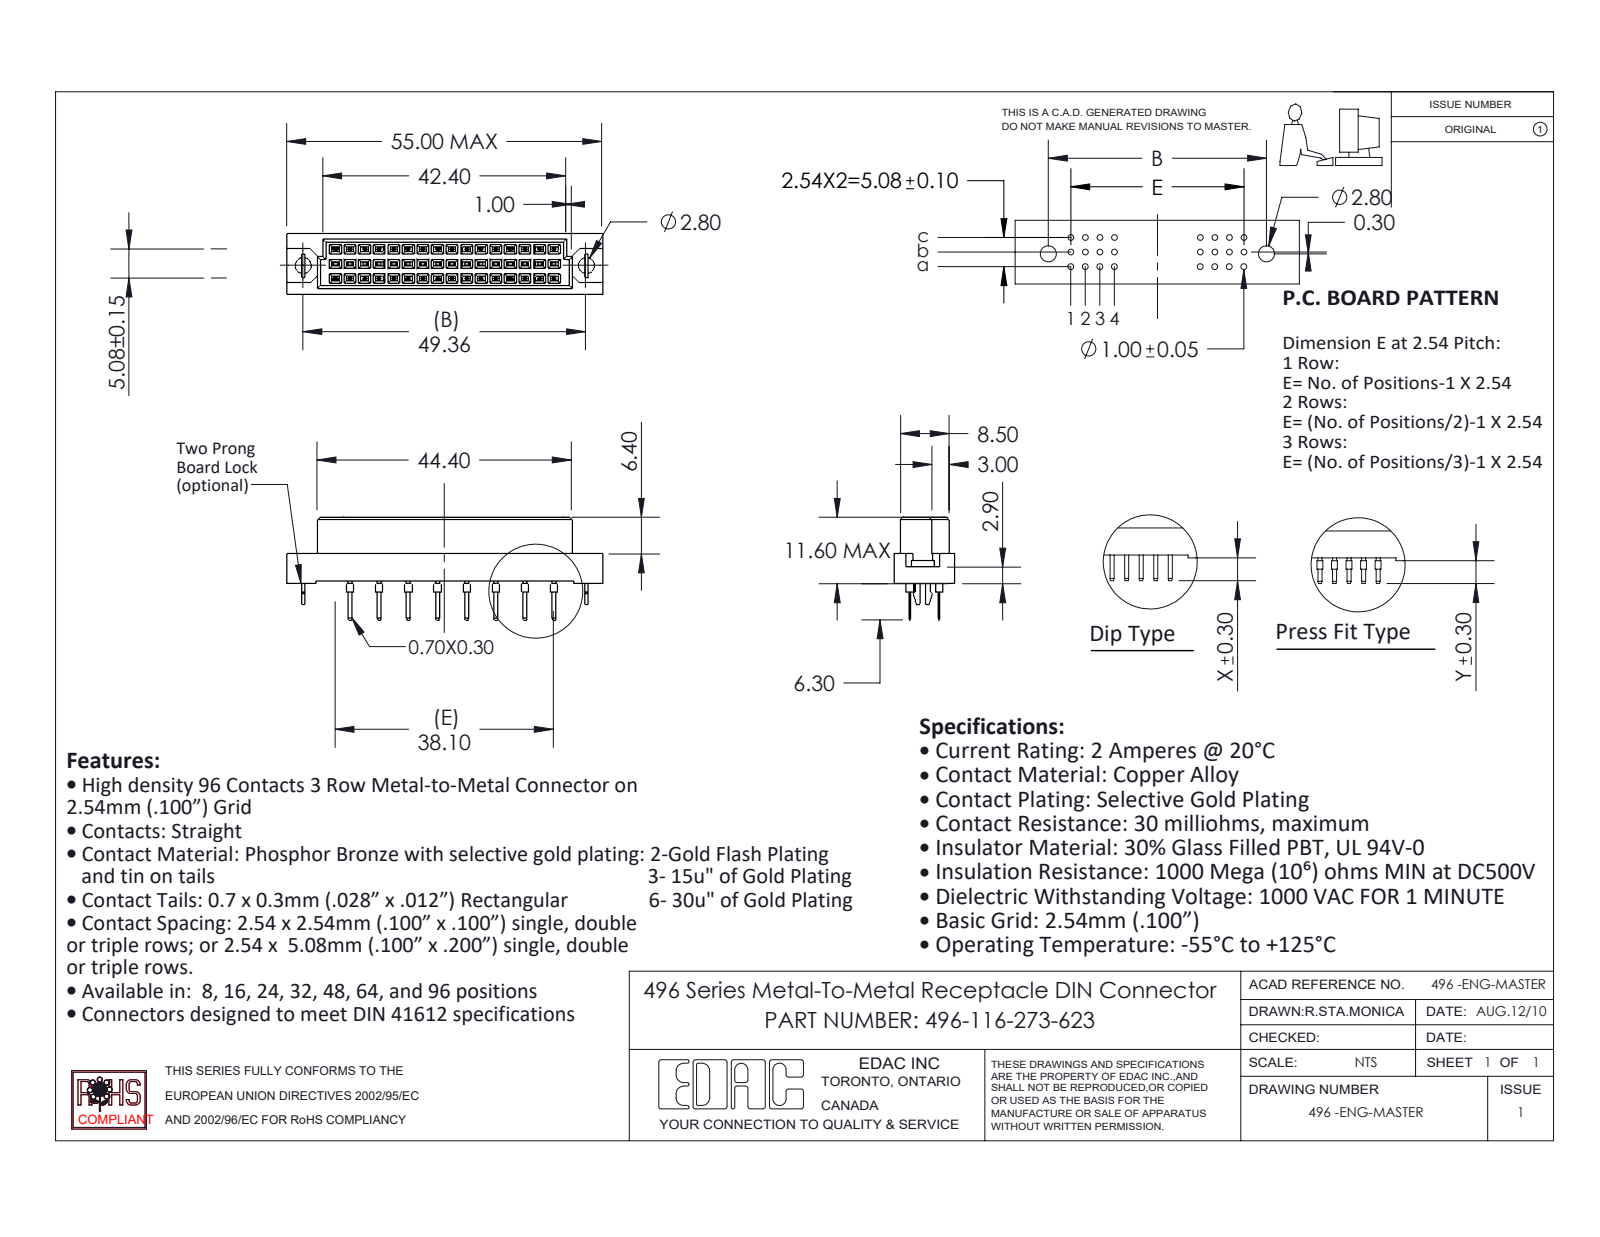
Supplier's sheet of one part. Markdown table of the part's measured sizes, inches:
| quantity | value |
| --- | --- |
| part name | 496 Part_48; 496-116-273-623; 496-290_73; 496 Bore-lock |
| STEP written by | SolidWorks 2020 (CONFIG_CONTROL_DESIGN) |
| units | inches |
| bodies | 19 solids, 990 faces (952 planar, 38 cylindrical, 0 other) |
| overall size | 2.165 × 0.705 × 0.417 |
| volume | 0.284 in³ |
| surface area | 7.318 in² |
| round holes (diameter × count) | 0.11 × 2 |
| round bosses / shafts (diameter × count) | 0.039 × 16 |
| partial cylindrical surfaces (radius × count) | 0.021 × 1 |
| main face-to-face distances | 0.1, 0.2, 0.041, 0.376, 0.032, 0.022, 0.417, 0.022, 0.132, 0.068 |
| hole center spacings | 1.943 |
